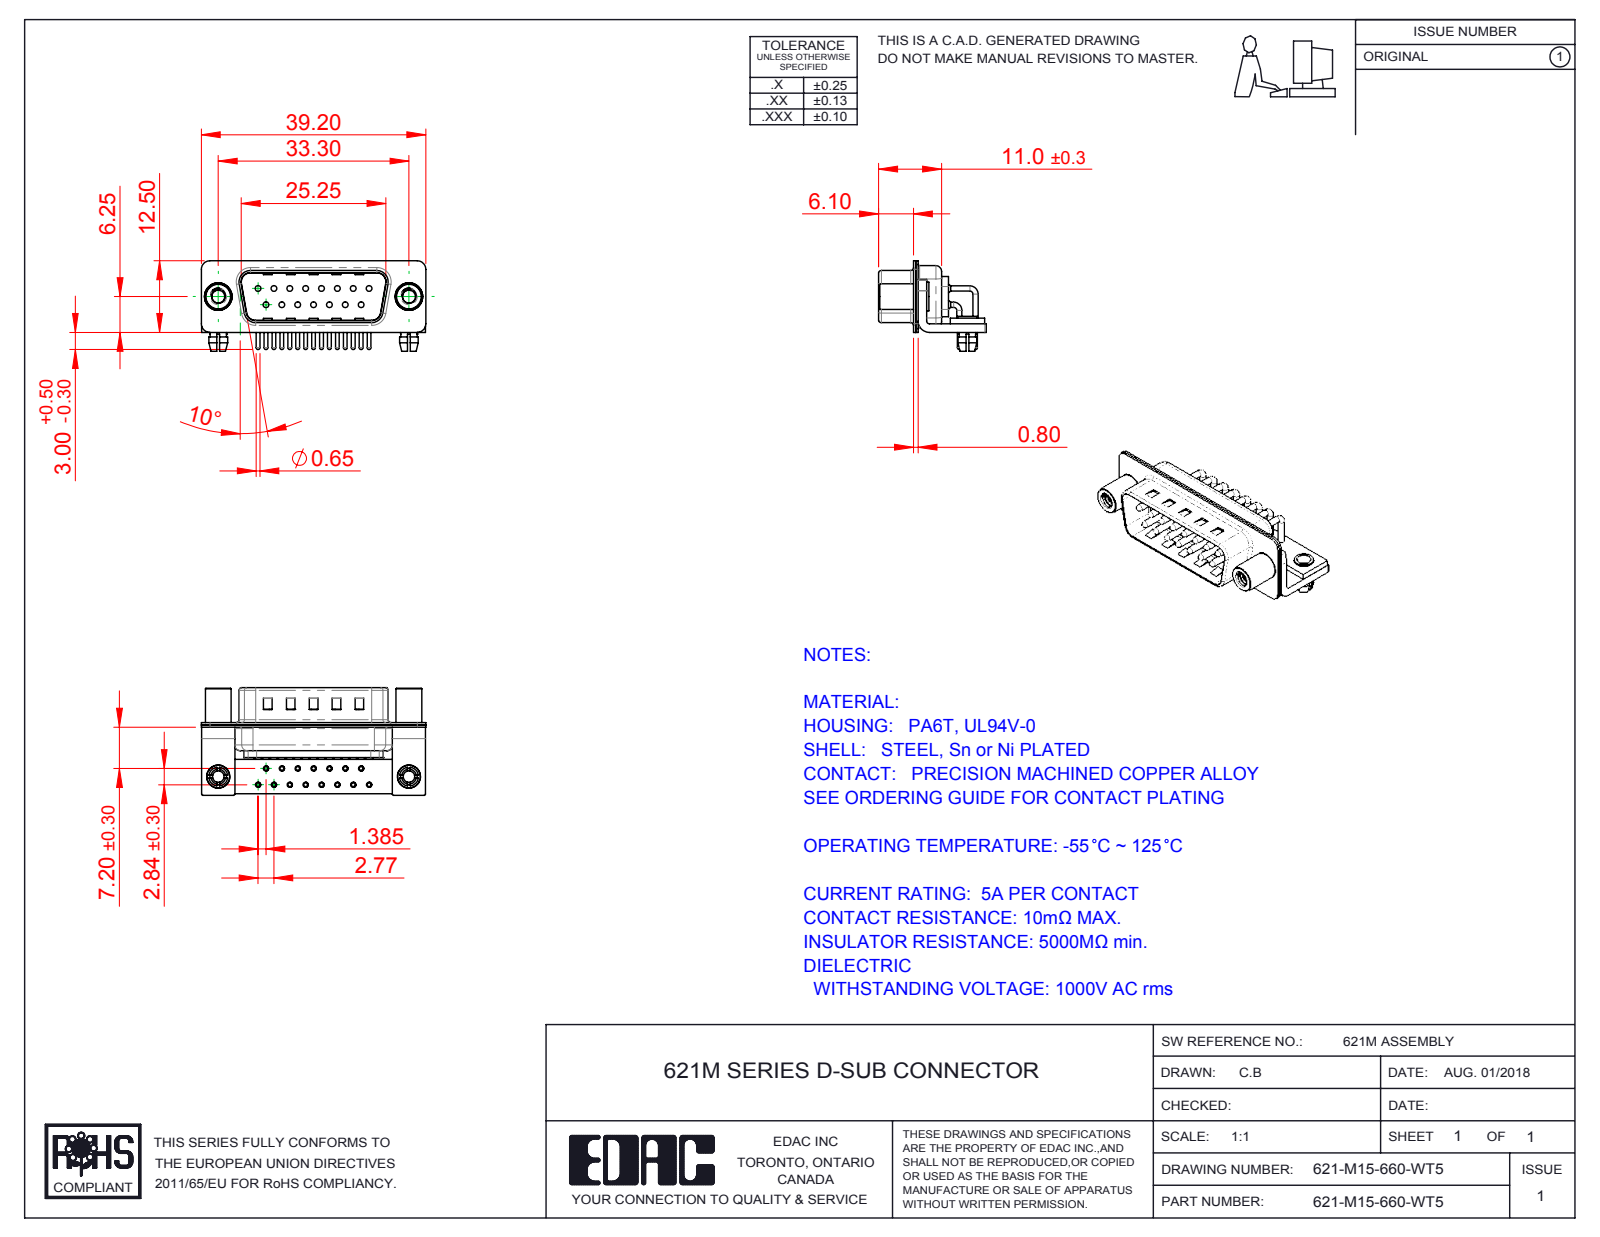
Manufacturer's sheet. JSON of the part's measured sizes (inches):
{"part_name": "621M 4-40 Threaded Standoff; 621M Stabilizer Bracket; 621M Housing_15 Contacts; 621M Shell Front_15 Contacts (+6 more)", "step_written_by": "SolidWorks 2016 (CONFIG_CONTROL_DESIGN)", "units": "inches", "bodies": {"solids": 25, "faces": 2212, "planar": 1175, "cylindrical": 799, "other": 238}, "overall_size": [1.543, 0.74, 0.622], "volume_in3": 0.155, "surface_area_in2": 10.72, "round_holes": [[0.079, 17], [0.035, 15], [0.039, 15], [0.067, 15], [0.089, 2], [0.098, 2], [0.126, 2], [0.157, 2], [0.189, 2]], "round_bosses_or_shafts": [[0.035, 22], [0.059, 15], [0.026, 15], [0.197, 2], [0.193, 2], [0.177, 2], [0.157, 2], [0.134, 2]], "partial_cylinders_radius": [[0.01, 16], [0.059, 16], [0.04, 15], [0.079, 13], [0.02, 9], [0.063, 8], [0.024, 4], [0.026, 4]], "face_to_face_distances": [0.016, 0.033, 0.059, 0.031, 0.049, 0.409, 0.376, 0.039, 0.075, 0.327], "hole_center_spacings": [0.124, 0.109, 0.218, 0.327, 0.436, 0.198, 0.198, 0.294]}
